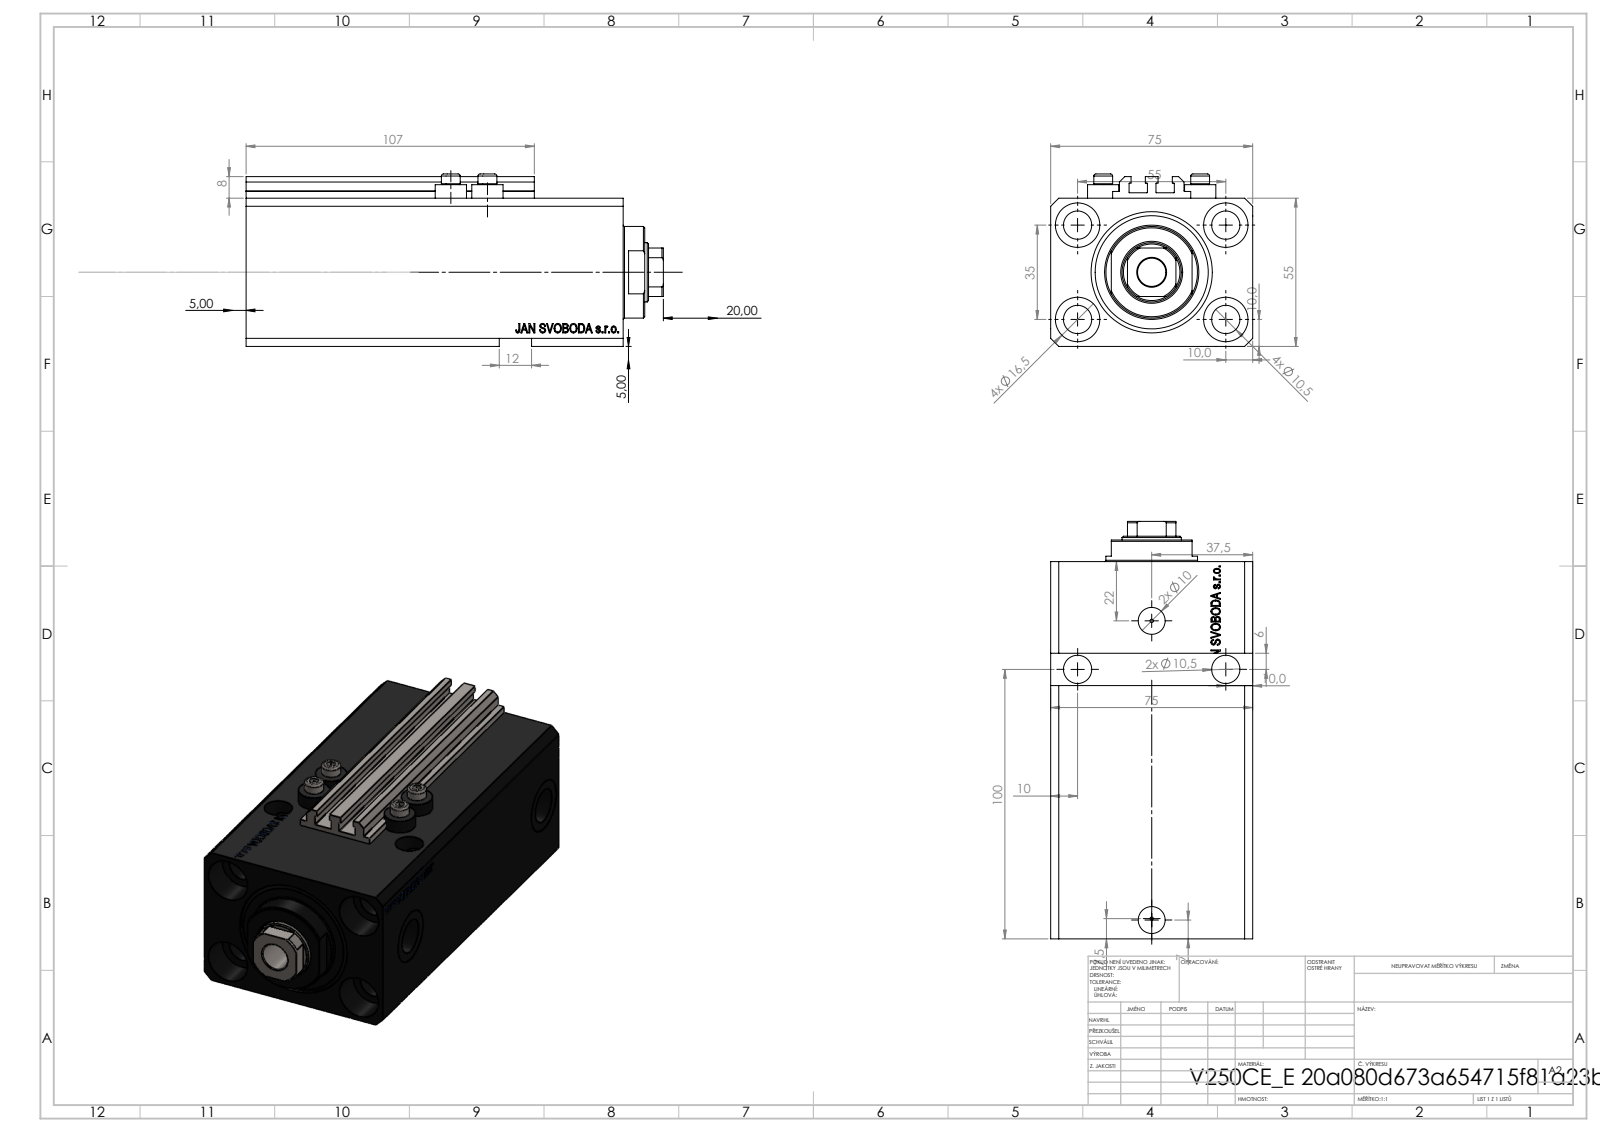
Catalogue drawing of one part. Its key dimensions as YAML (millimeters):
part_name: "V250CE_C_VCP; V250CE_E_Body; ALLEN BOLT V250CE; V250CE_VC_E"
step_written_by: "SolidWorks 2019 (CONFIG_CONTROL_DESIGN)"
units: millimeters
bodies: {solids: 8, faces: 1084, planar: 514, cylindrical: 146, other: 424}
overall_size: [155, 75, 64]
volume: 485219
surface_area: 115303
round_holes:
  - {diameter: 10.5, count: 9}
  - {diameter: 1.25, count: 4}
  - {diameter: 4, count: 4}
  - {diameter: 16.5, count: 4}
  - {diameter: 10, count: 2}
  - {diameter: 13.16, count: 2}
  - {diameter: 20, count: 2}
  - {diameter: 22, count: 1}
  - {diameter: 32, count: 1}
  - {diameter: 45, count: 1}
round_bosses_or_shafts:
  - {diameter: 11.6, count: 4}
  - {diameter: 7, count: 4}
  - {diameter: 34, count: 1}
partial_cylinders:
  - {radius: 0.2, count: 10}
  - {radius: 10.5, count: 1}
face_to_face_distances: [55, 75, 15, 140, 125, 3, 9.9, 57, 115.1, 130.1]
hole_center_spacings: [32.6, 32.87, 55, 96.98, 13.6, 14.09, 25.81, 32.58]
